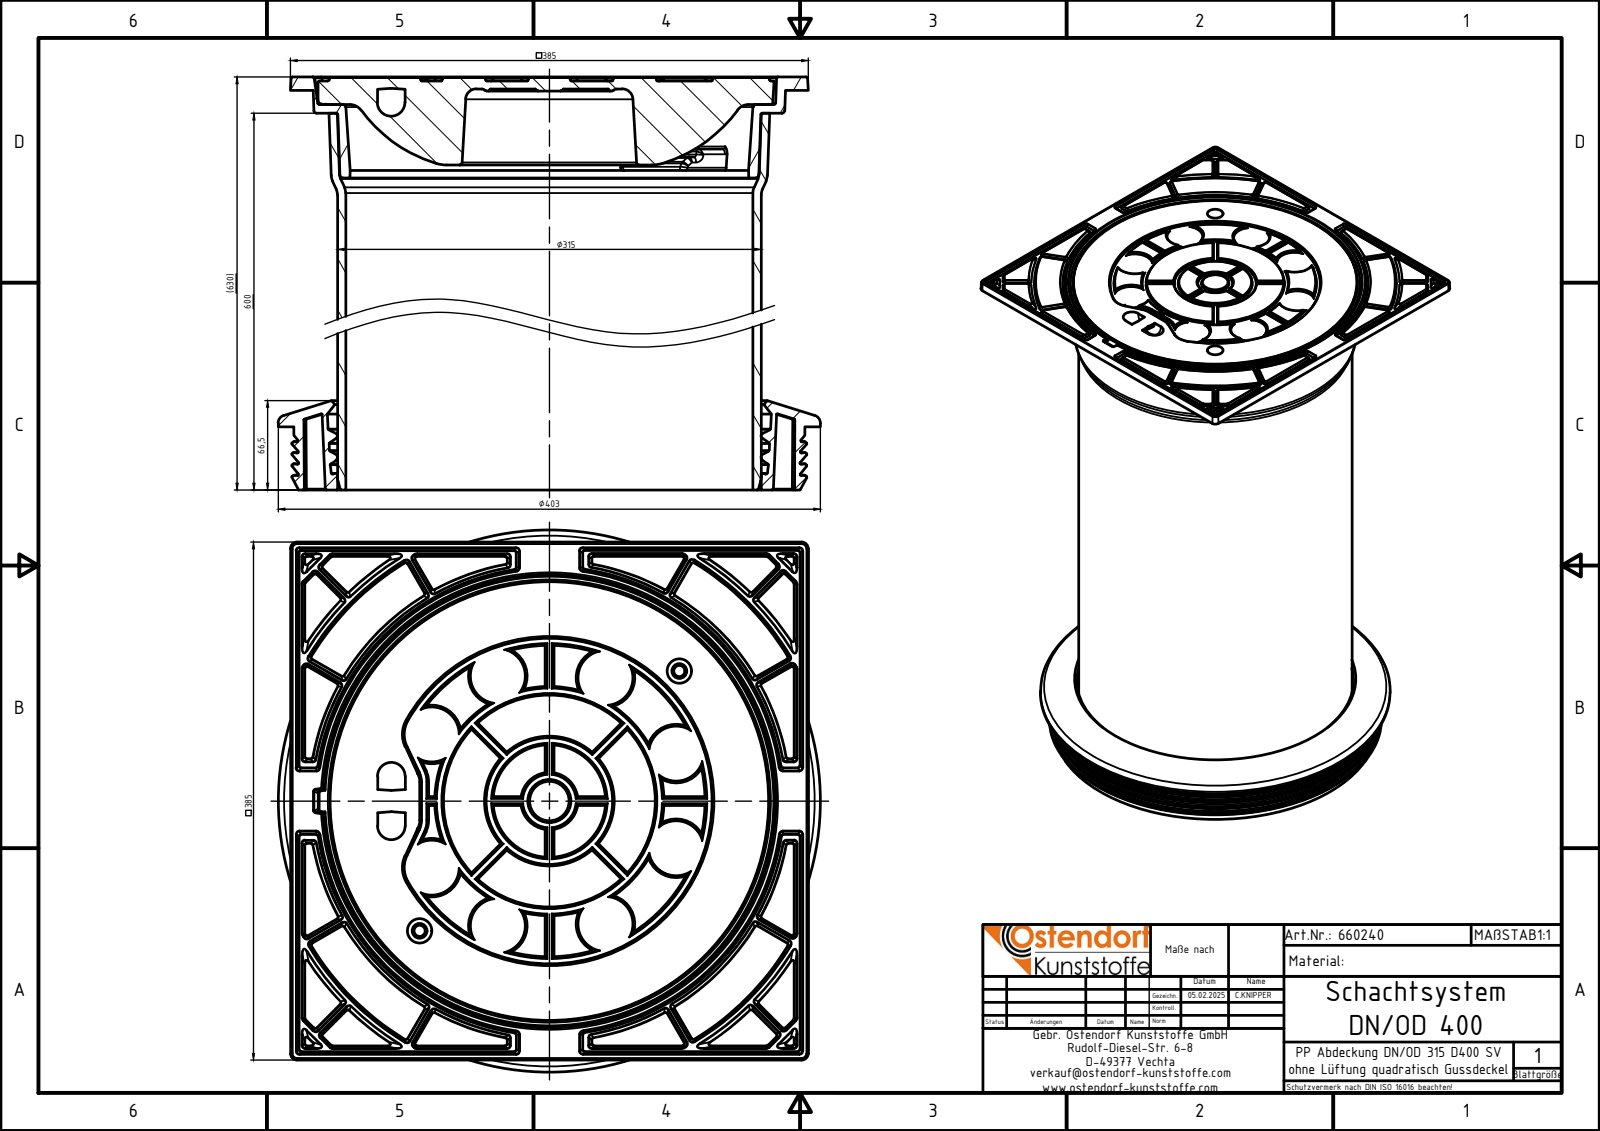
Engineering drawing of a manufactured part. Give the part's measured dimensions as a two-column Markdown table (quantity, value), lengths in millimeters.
| quantity | value |
| --- | --- |
| part name | 660240z; 660300z; 660500_05.02.25z; 990055z (+1 more) |
| STEP written by | Autodesk Inventor 2024 (AUTOMOTIVE_DESIGN) |
| units | millimeters |
| bodies | 4 solids, 1769 faces (241 planar, 355 cylindrical, 1173 other) |
| overall size | 627 × 403 × 403 |
| volume | 9 089 000 mm³ |
| surface area | 2 128 000 mm² |
| round holes (diameter × count) | 8.38 × 2, 11 × 2, 18 × 2, 302.6 × 1, 315 × 1 |
| round bosses / shafts (diameter × count) | 403 × 1, 380 × 1 |
| partial cylindrical surfaces (radius × count) | 1 × 204, 2.5 × 48, 0.5 × 14, 4 × 8, 2 × 4, 3 × 1 |
| main face-to-face distances | 9.5, 0.5, 10, 10.5, 20.5, 20, 6.5, 2.5, 17, 26.5 |
| hole center spacings | 136.5, 136.51, 273.01 |
